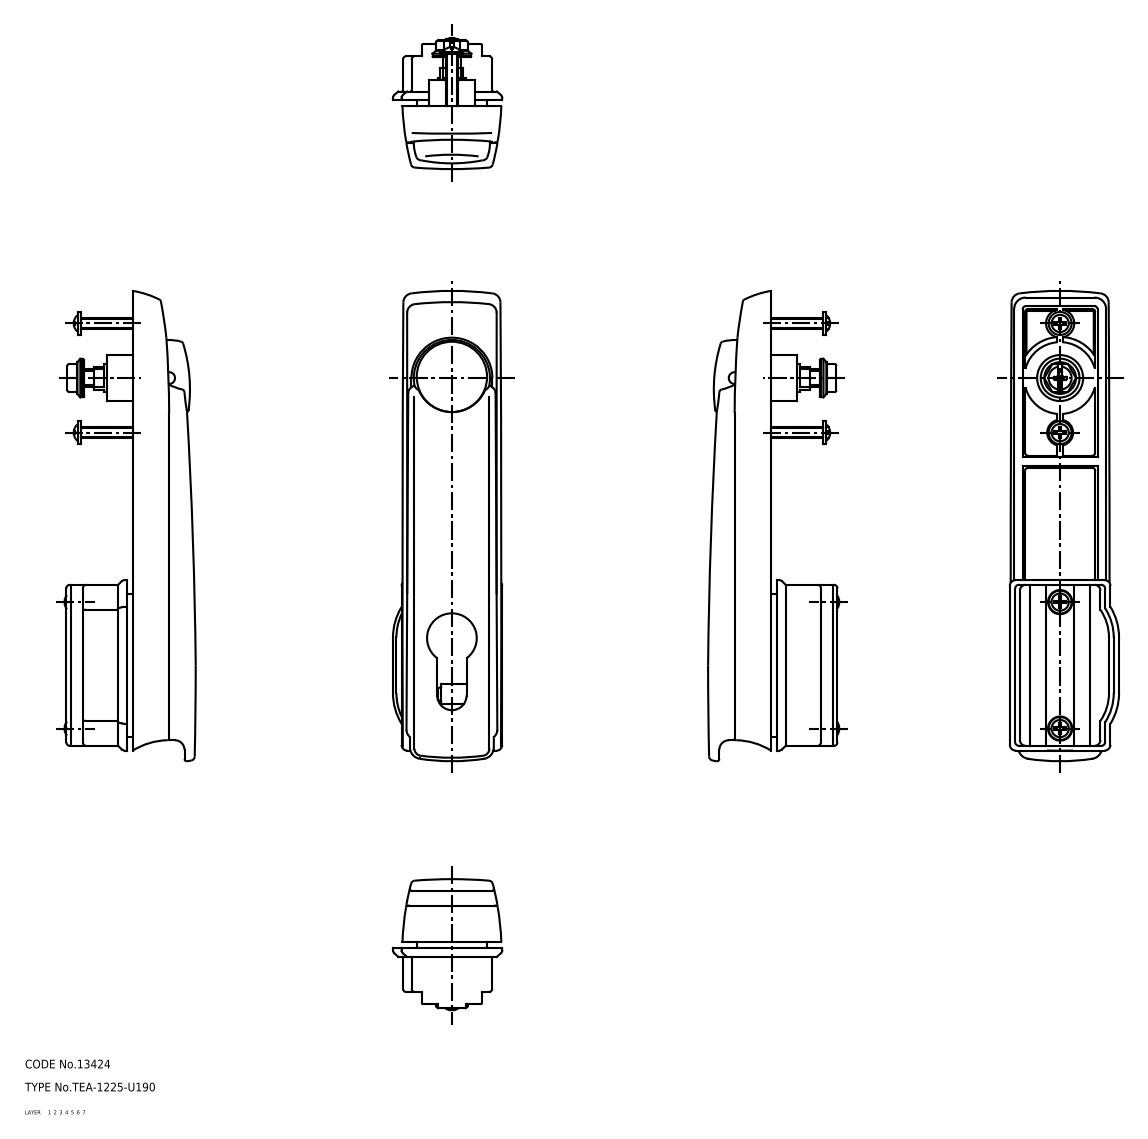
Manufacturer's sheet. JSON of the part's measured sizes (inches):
{"part_name": "handle; bracket; base; shaft (+1 more)", "step_written_by": "CADfix (AUTOMOTIVE_DESIGN)", "units": "inches", "bodies": {"solids": 4, "faces": 507, "planar": 0, "cylindrical": 0, "other": 507}, "overall_size": [6.443, 1.853, 1.496], "volume_in3": 5.437, "surface_area_in2": 71.87}
